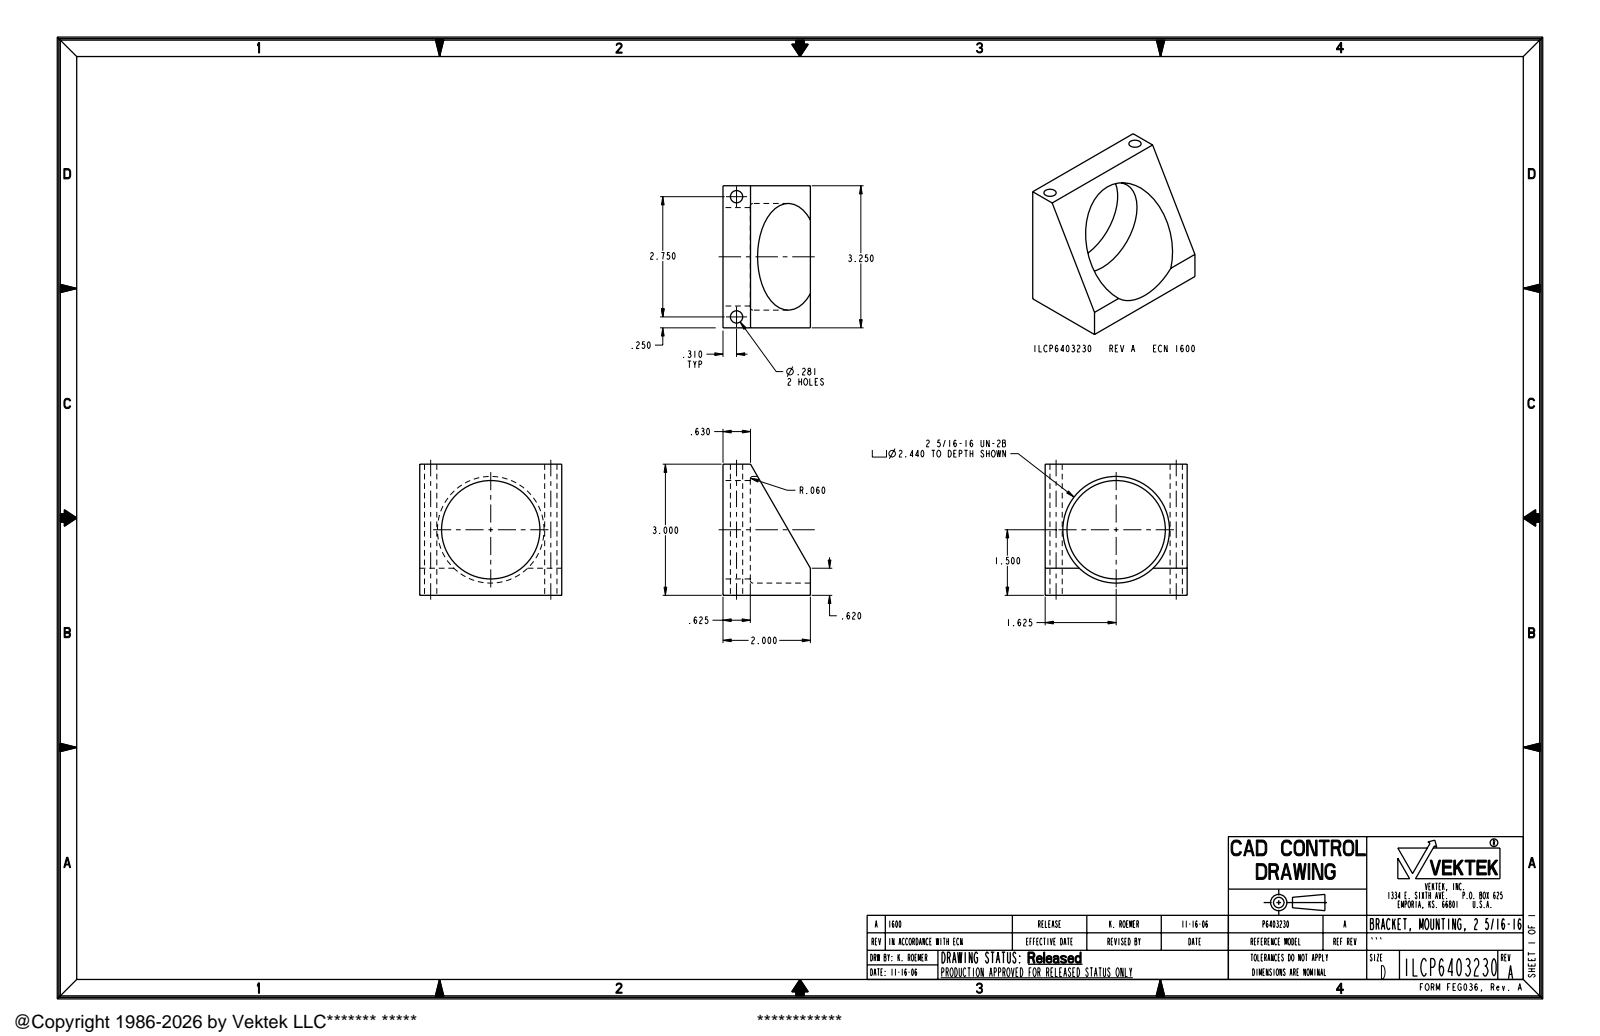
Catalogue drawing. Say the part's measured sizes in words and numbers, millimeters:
The part is named "ILCP6403230". Its 3-D file was written by "PRO/ENGINEER BY PARAMETRIC TECHNOLOGY CORPORATION, 2005180 (AUTOMOTIVE_DESIGN_CC2)". It is 1 solid with 18 faces: 8 planar, 8 cylindrical and 2 other. Overall it measures 82.6 by 76.2 by 50.8 millimeters. Its volume is 119 900 cubic millimeters and its surface area 29 060 square millimeters. Round holes: 2 of diameter 7.1, 1 of diameter 57.2, 1 of diameter 62. The main face-to-face distances are 82.6, 76.2, 50.8, 34.9, 15.9. The hole center spacings are 69.9.
